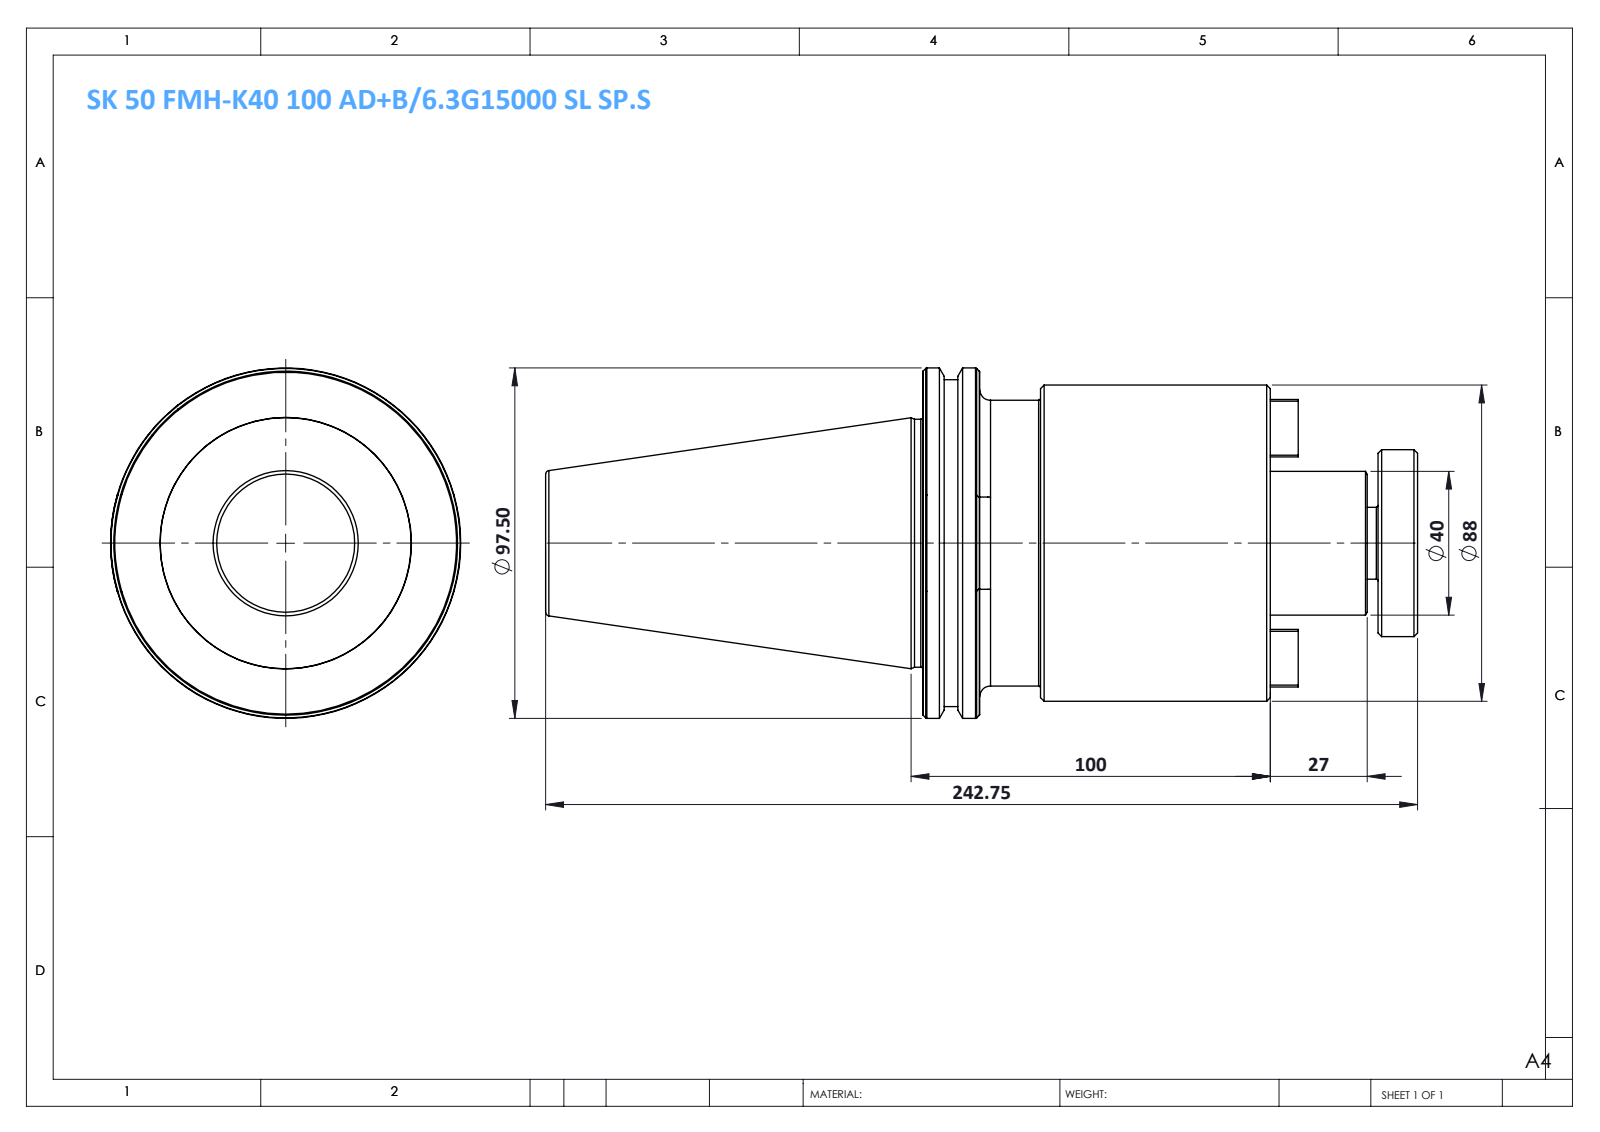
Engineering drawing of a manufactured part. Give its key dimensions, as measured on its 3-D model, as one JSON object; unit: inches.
{"part_name": "SK50 FMH40 100 AD-6.3G15000 SL SP.S", "step_written_by": "SolidWorks 2014 (CONFIG_CONTROL_DESIGN)", "units": "inches", "bodies": {"solids": 1, "faces": 115, "planar": 28, "cylindrical": 18, "other": 69}, "overall_size": [9.557, 3.839, 3.839], "volume_in3": 55.47, "surface_area_in2": 108.1, "round_bosses_or_shafts": [[3.839, 1], [3.583, 1], [3.465, 1], [3.13, 1], [2.717, 1], [2.047, 1], [1.575, 1], [0.787, 1]], "face_to_face_distances": [3.811, 1.614, 5.425, 0.433, 1.181, 4.992, 4.799, 4.366, 3.185, 0.626]}
